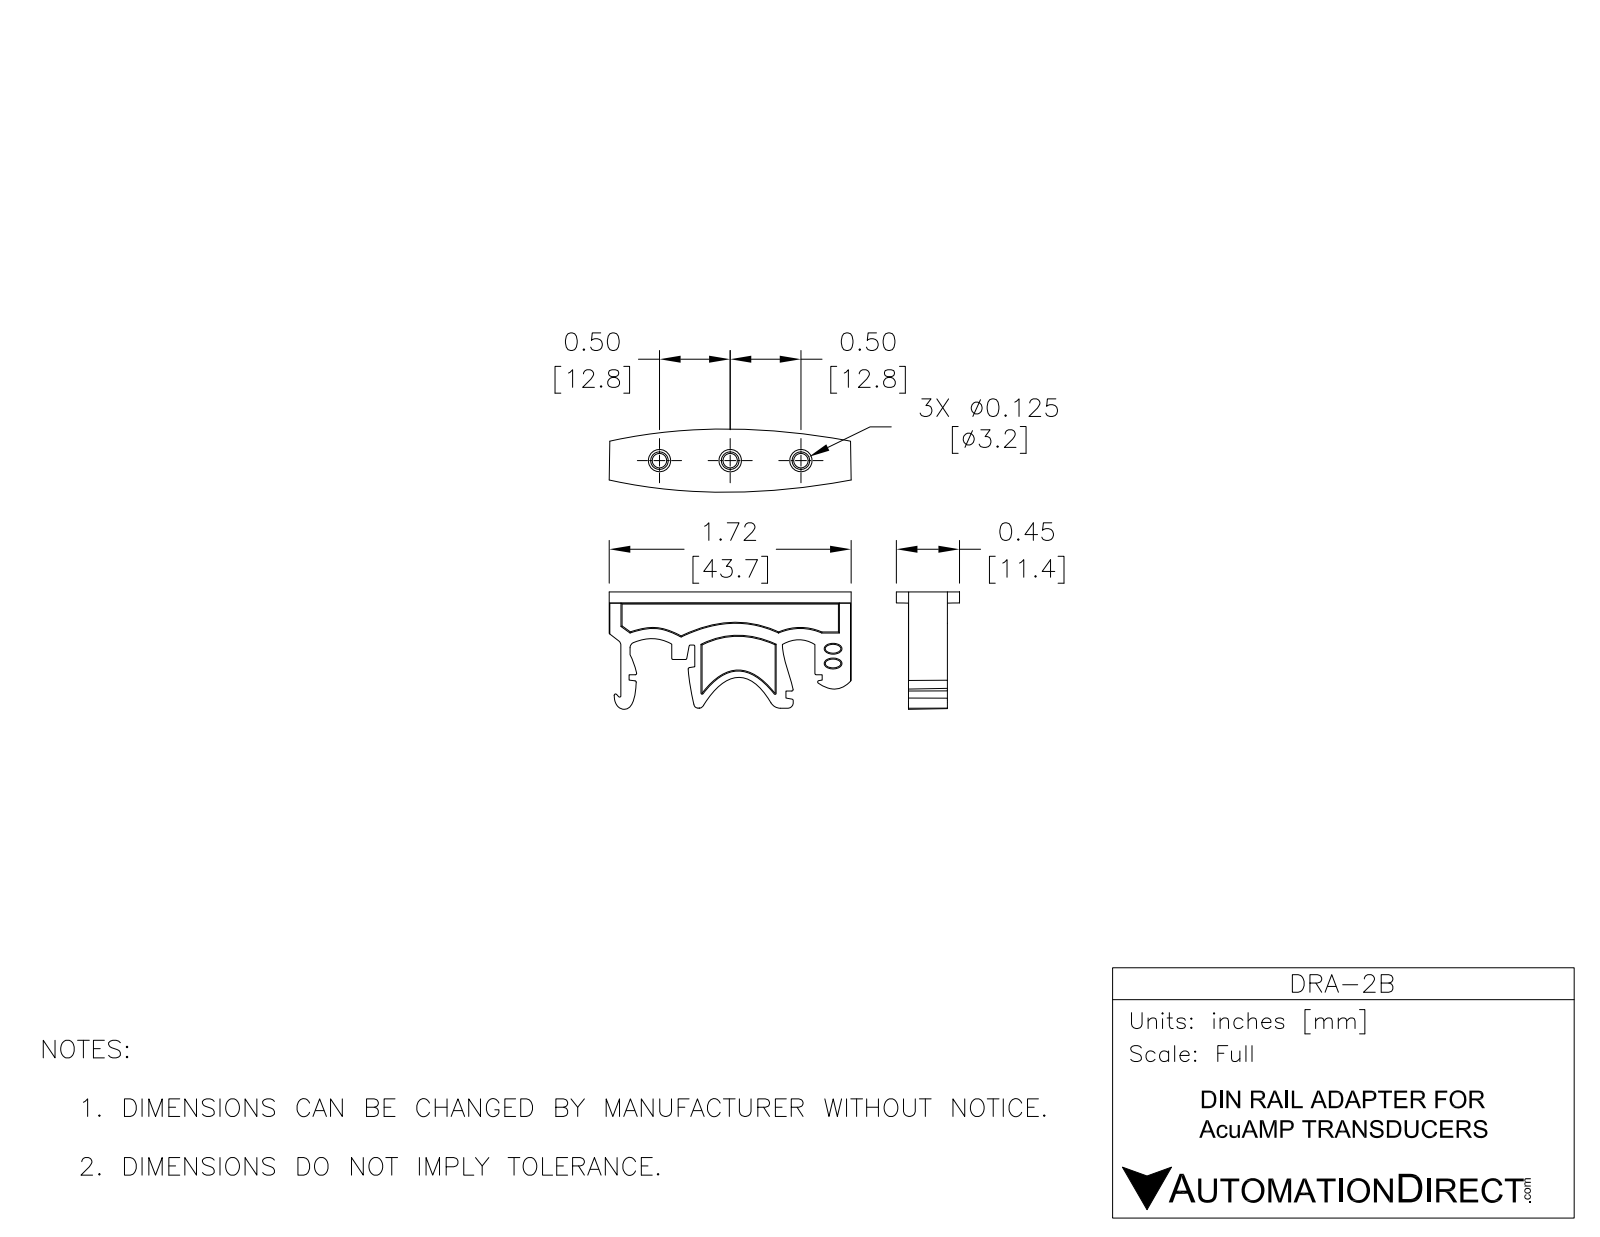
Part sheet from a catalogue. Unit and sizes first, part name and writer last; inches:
Units: inches
Overall size (bounding box): 1.72 × 0.833 × 0.449
Partial cylindrical surfaces — rounded edges, fillets, slot ends (radius × count): R0.01 ×3, R0.01 ×3, R0.039 ×1, R0.039 ×1
Main face-to-face distances: 0.277, 0.237, 0.02, 0.257, 0.257, 0.02, 1.462, 0.608, 0.854, 0.444
Volume: 0.222 in³ · Surface area: 5.047 in²
Bodies: 1 solid, 108 faces (47 planar, 8 cylindrical, 53 other)
Part name (STEP PRODUCT): DINclip10(4.sanslogo)
STEP written by: SolidWorks 2015 (CONFIG_CONTROL_DESIGN)
